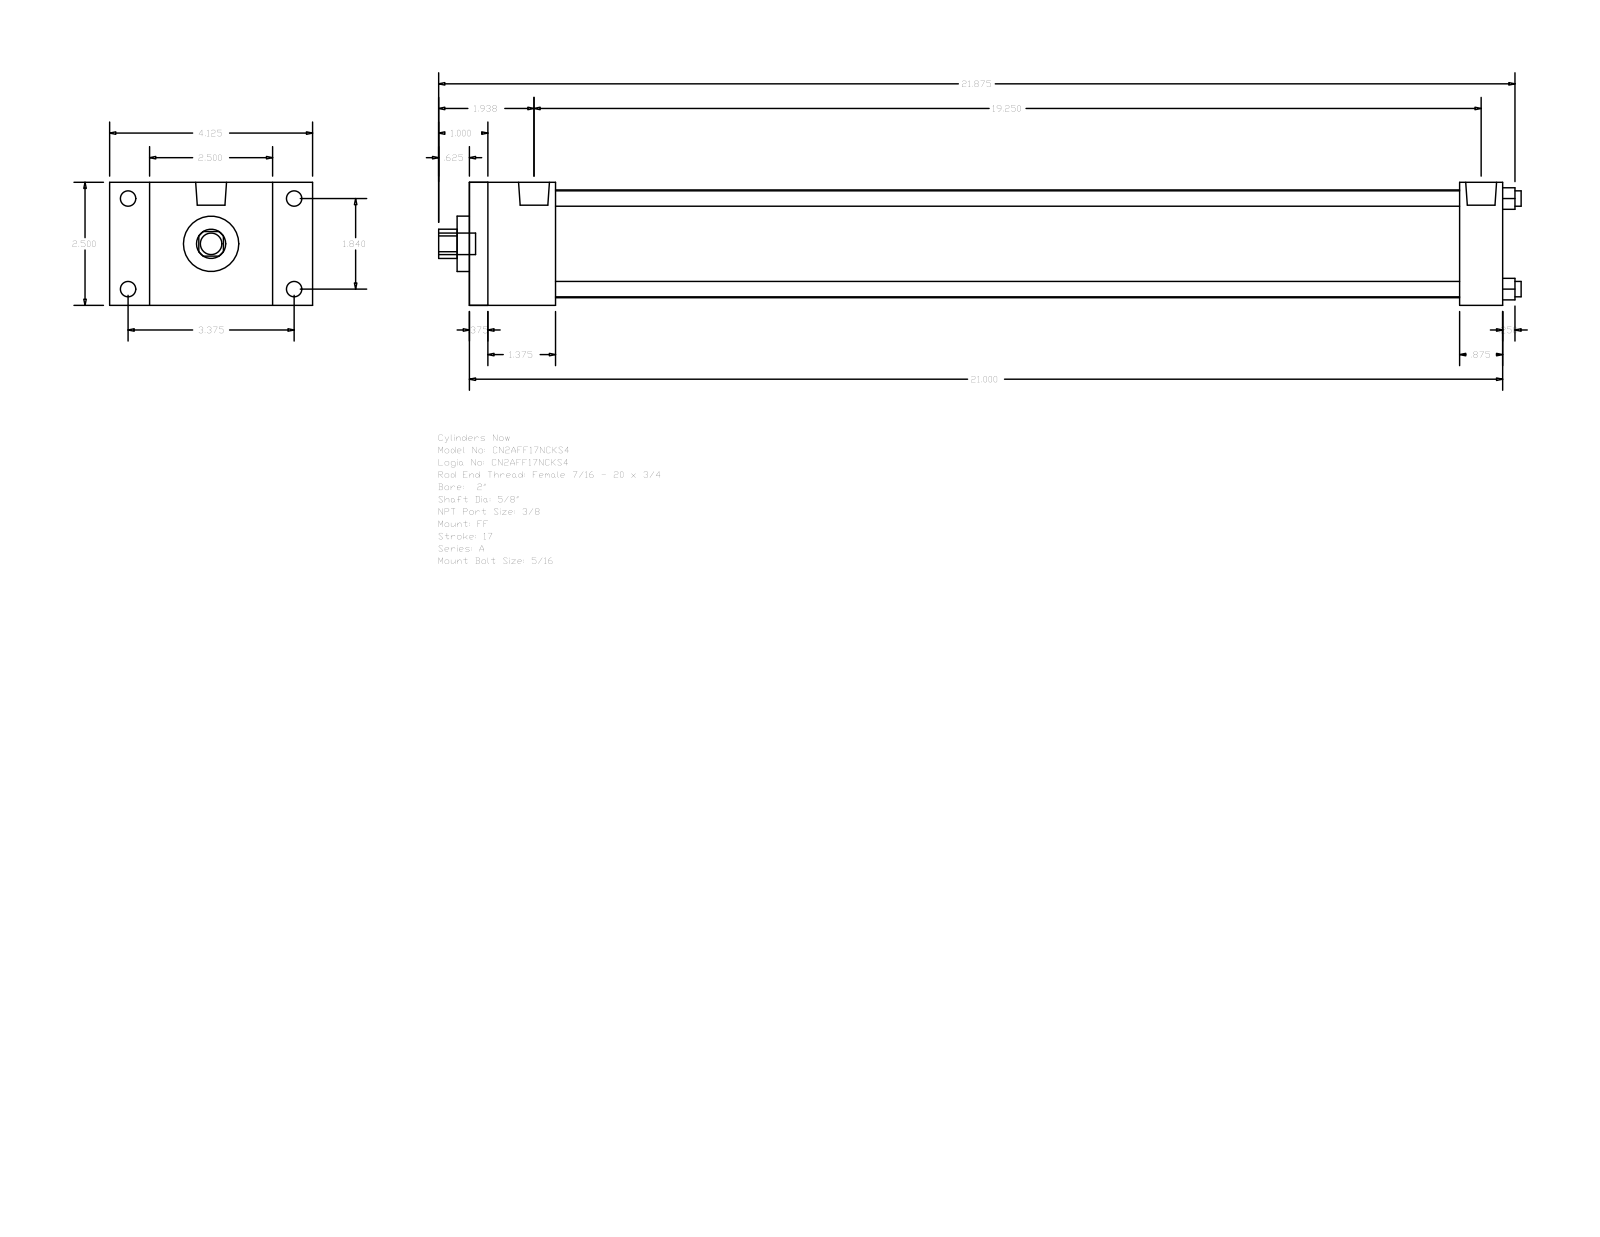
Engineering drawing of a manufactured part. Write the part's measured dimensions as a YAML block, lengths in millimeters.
part_name: "A_FF__0200_0.625"
step_written_by: "GSSL Pune (CONFIG_CONTROL_DESIGN)"
units: millimeters
bodies: {solids: 0, faces: 92, planar: 64, cylindrical: 28, other: 0}
overall_size: [558.8, 104.78, 63.5]
round_holes:
  - {diameter: 7.94, count: 4}
  - {diameter: 15.88, count: 1}
  - {diameter: 28.57, count: 1}
  - {diameter: 55.63, count: 1}
round_bosses_or_shafts:
  - {diameter: 7.94, count: 4}
  - {diameter: 5.56, count: 4}
  - {diameter: 15.93, count: 2}
  - {diameter: 11.11, count: 1}
partial_cylinders:
  - {radius: 7.54, count: 1}
face_to_face_distances: [63.5, 533.39, 9.52, 523.87, 44.45, 511.17, 34.93, 501.65, 466.72, 488.94]
hole_center_spacings: [33.05, 46.74, 66.1]
